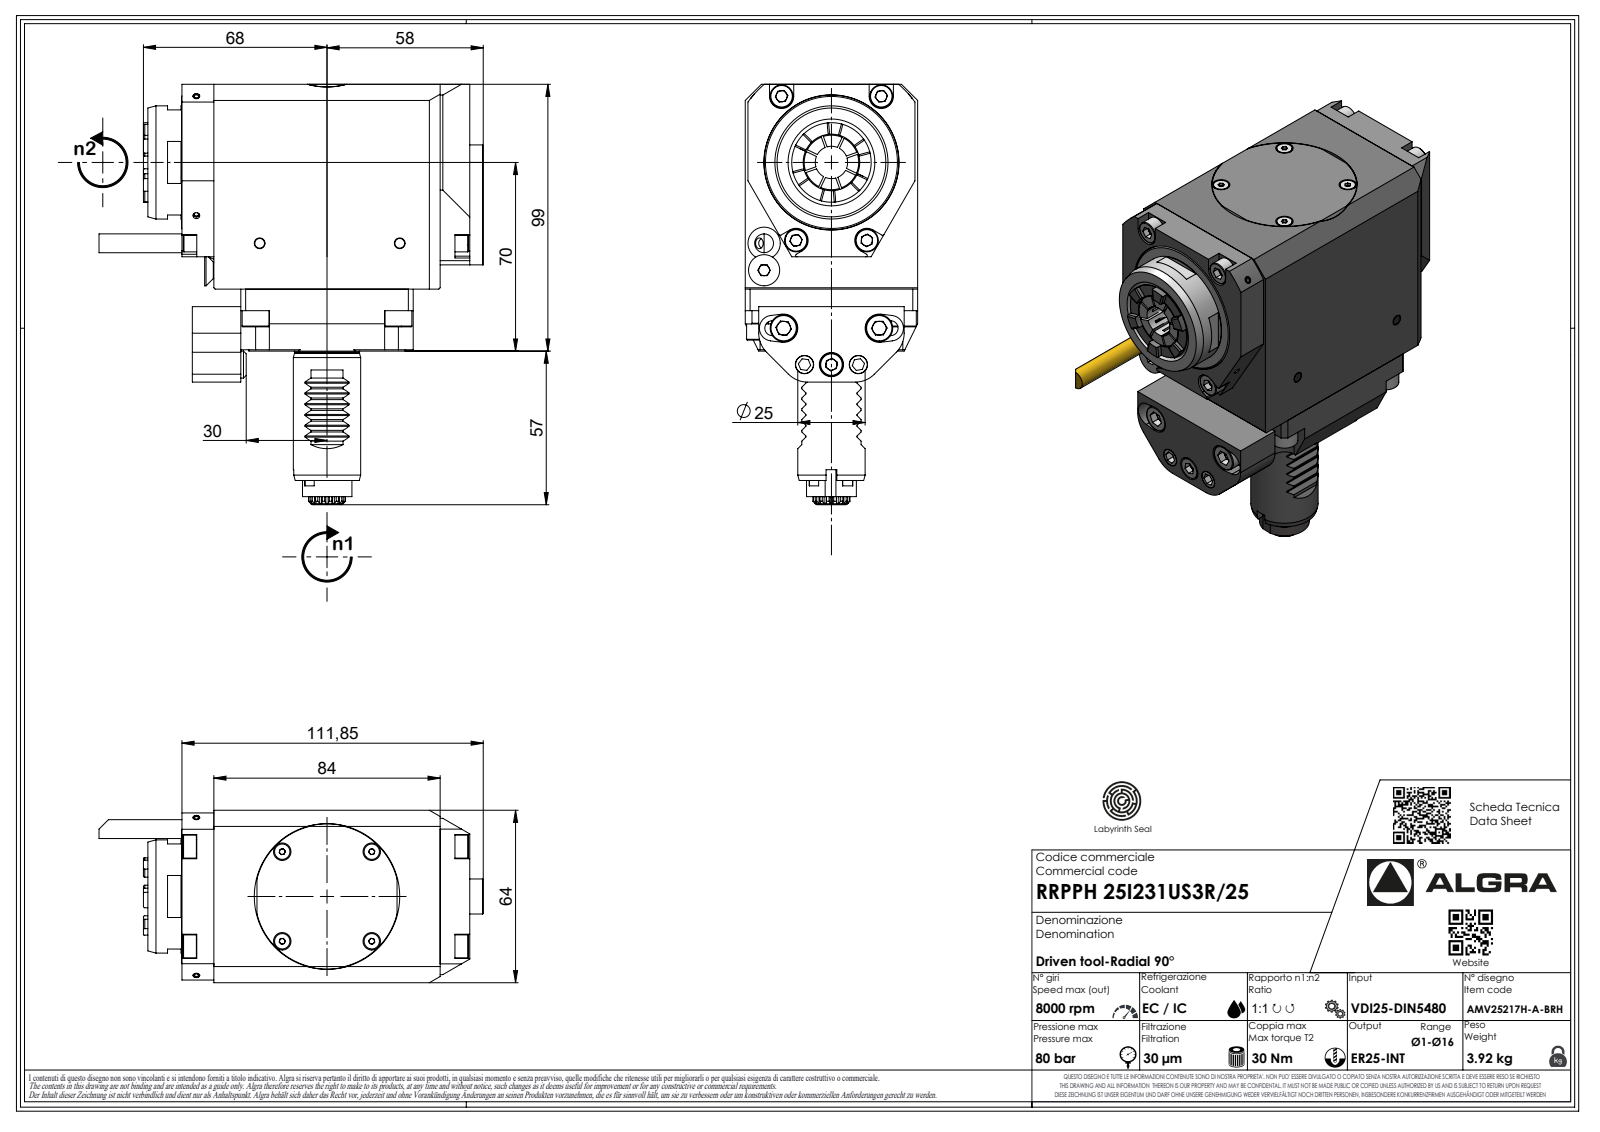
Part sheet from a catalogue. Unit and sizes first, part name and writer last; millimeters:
Units: millimetres
Overall size (bounding box): 161 × 145.5 × 64
Round holes (diameter × count): ⌀2.1 ×1, ⌀4 ×1, ⌀18.7 ×1, ⌀21 ×1, ⌀22 ×1, ⌀30.5 ×1
Round bosses / shafts (diameter × count): ⌀42 ×1, ⌀29.5 ×1, ⌀25 ×1, ⌀24.1 ×1, ⌀19.27 ×1, ⌀18.5 ×1, ⌀7 ×1, ⌀6.37 ×1
Partial cylindrical surfaces — rounded edges, fillets, slot ends (radius × count): R0.3 ×12, R35 ×8, R0.33 ×7, R0.52 ×7, R3.7 ×7, R0.5 ×6, R4.5 ×4, R5.1 ×4
Main face-to-face distances: 64, 104, 10, 74, 23, 95.85, 95, 84, 0.5, 6.5
Volume: 640 586 mm³ · Surface area: 57 537 mm²
Bodies: 1 solid, 821 faces (507 planar, 144 cylindrical, 170 other)
Part name (STEP PRODUCT): RRPPH25I131US325
STEP written by: SolidWorks 2023 (AUTOMOTIVE_DESIGN)
